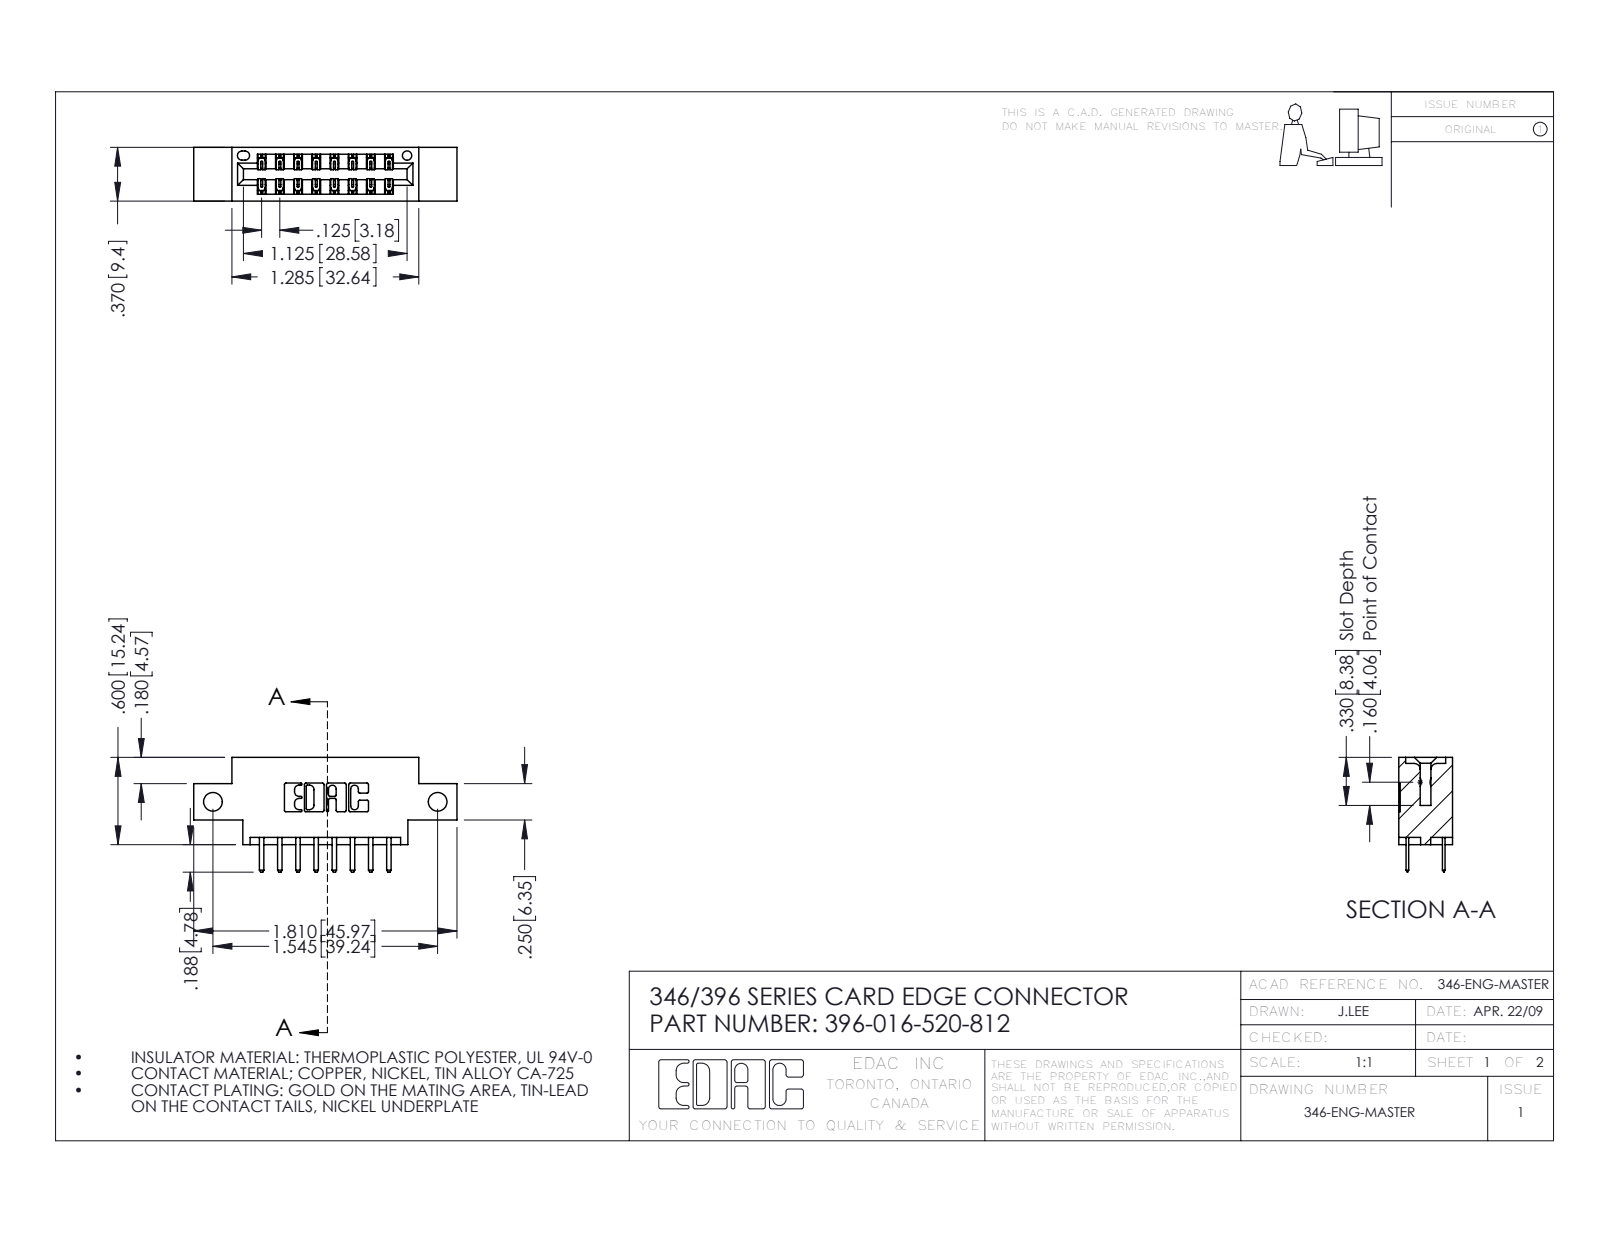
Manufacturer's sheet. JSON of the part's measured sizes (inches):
{"part_name": "346 Part_0.170 Offset - Side Mount; 345-292-001_345-293-120; 396-016-520-812", "step_written_by": "SolidWorks 2016 (CONFIG_CONTROL_DESIGN)", "units": "inches", "bodies": {"solids": 17, "faces": 1022, "planar": 672, "cylindrical": 350, "other": 0}, "overall_size": [1.81, 0.788, 0.37], "volume_in3": 0.242, "surface_area_in2": 7.67, "round_holes": [[0.128, 2], [0.064, 1]], "partial_cylinders_radius": [[0.006, 24], [0.01, 22], [0.01, 20], [0.007, 6], [0.031, 6], [0.026, 3], [0.014, 2], [0.022, 2]], "face_to_face_distances": [0.25, 0.37, 0.048, 0.322, 0.148, 0.222, 0.1, 0.174, 0.275, 0.072], "hole_center_spacings": [1.545]}
